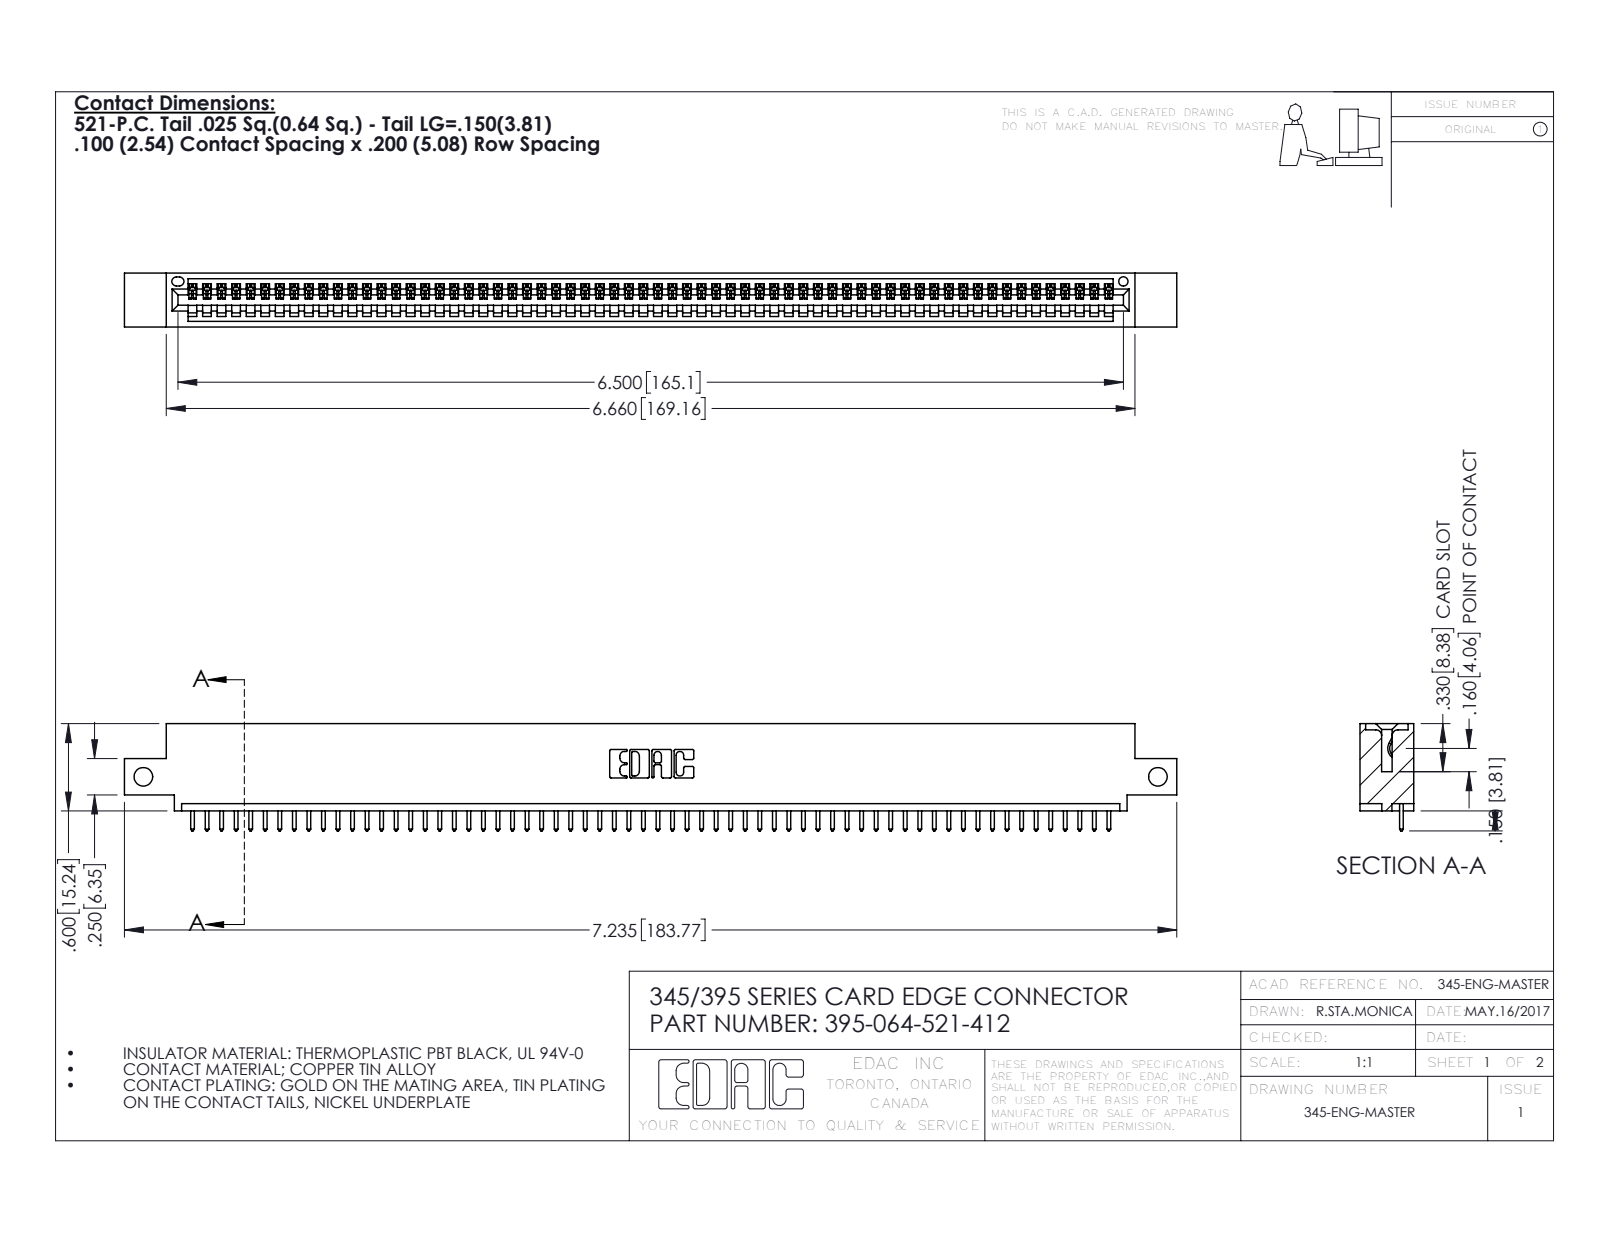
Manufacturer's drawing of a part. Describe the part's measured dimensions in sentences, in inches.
The part is named "345 Part_0.110 Offset - Side Mount; 395-064-521-412; 345-292-001_345-293-121". Its 3-D file was written by "SolidWorks 2016 (CONFIG_CONTROL_DESIGN)". It is 65 solids with 3842 faces: 2644 planar, 1198 cylindrical and 0 other. Overall it measures 7.235 by 0.737 by 0.37 inches. Its volume is 1.055 cubic inches and its surface area 34.88 square inches. Round holes: 2 of diameter 0.128, 1 of diameter 0.064. Partial cylindrical surfaces (rounded edges, fillets, slot ends): 128 of radius 0.006, 128 of radius 0.01, 22 of radius 0.01, 6 of radius 0.007, 6 of radius 0.031, 3 of radius 0.026, 2 of radius 0.031, 2 of radius 0.04. The main face-to-face distances are 0.298, 0.072, 0.37, 0.2, 0.098, 0.272, 0.025, 0.225, 0.149, 0.072. The hole center spacings are 6.975.
